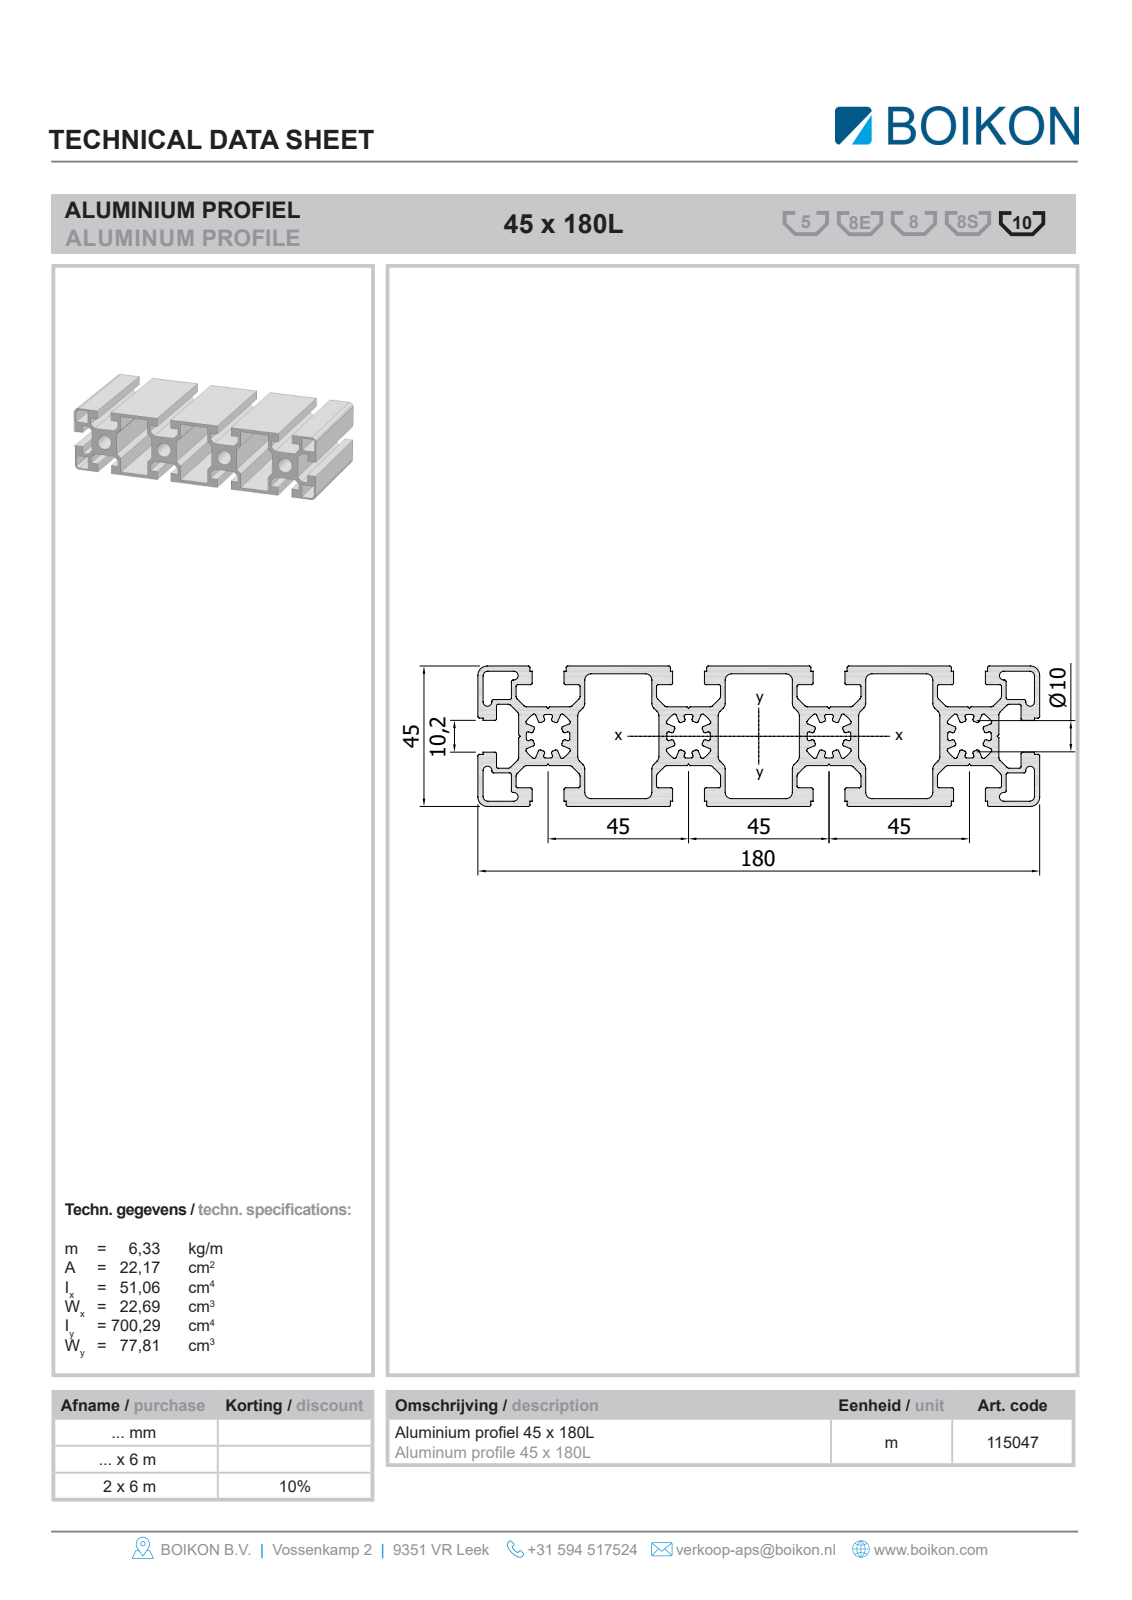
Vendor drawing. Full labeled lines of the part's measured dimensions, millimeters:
Part name (STEP PRODUCT): Root; 11504745x180LBOIKON0
STEP written by: HiCAD 2013 1802.4 Build 509 (AUTOMOTIVE_DESIGN)
Units: millimetres
Bodies: 1 solid, 170 faces (158 planar, 12 cylindrical, 0 other)
Overall size (bounding box): 1000 × 180 × 45
Volume: 2 676 000 mm³ · Surface area: 1 533 000 mm²
Round holes (diameter × count): ⌀10.2 ×4
Partial cylindrical surfaces — rounded edges, fillets, slot ends (radius × count): R2 ×4, R3 ×4
Main face-to-face distances: 45, 13.1, 31.9, 2.12, 42.88, 18.8, 10.98, 29.78, 90, 6
Hole centre spacings: 45, 90, 135
